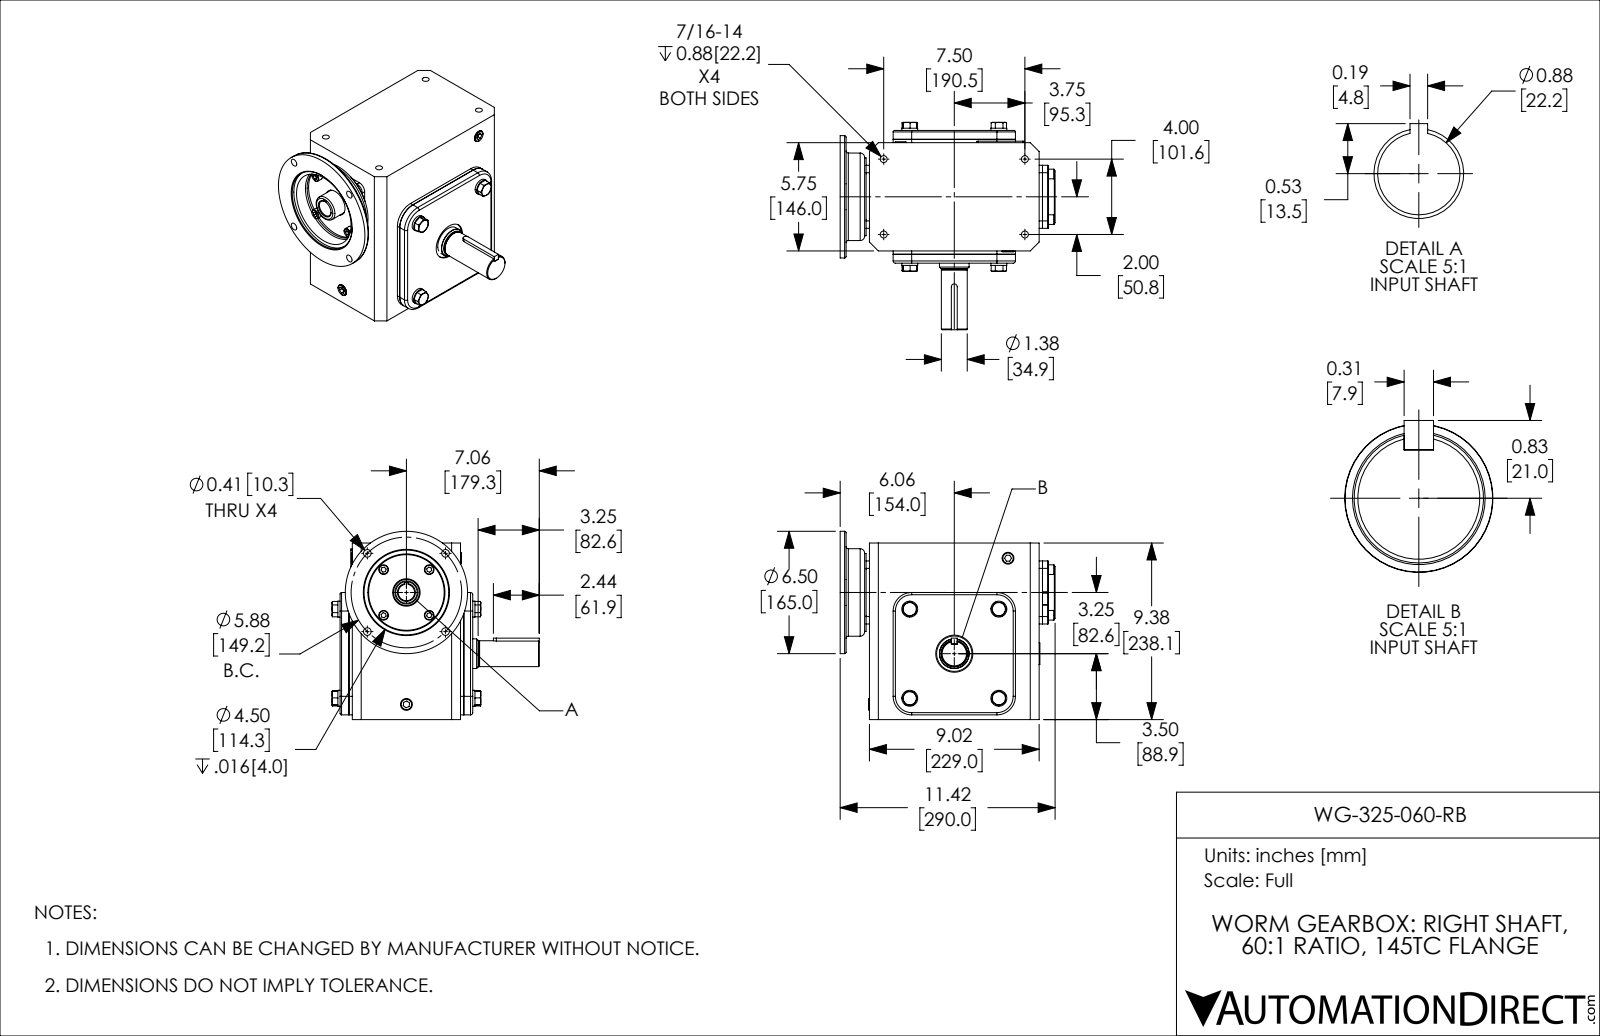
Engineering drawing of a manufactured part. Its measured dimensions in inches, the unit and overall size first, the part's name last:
Units: inches
Overall size (bounding box): 11.417 × 11.014 × 9.998
Round holes (diameter × count): ⌀0.368 ×4, ⌀0.406 ×4, ⌀0.628 ×3, ⌀0.591 ×1, ⌀0.875 ×1, ⌀0.978 ×1, ⌀1.181 ×1, ⌀1.457 ×1, ⌀1.969 ×1, ⌀2.441 ×1, ⌀2.756 ×1, ⌀4.016 ×1
Round bosses / shafts (diameter × count): ⌀0.846 ×4, ⌀0.512 ×4, ⌀6.496 ×1, ⌀4.646 ×1, ⌀4.134 ×1, ⌀2.835 ×1, ⌀1.575 ×1, ⌀1.378 ×1
Partial cylindrical surfaces — rounded edges, fillets, slot ends (radius × count): R0.079 ×11, R0.118 ×4, R0.394 ×4, R0.906 ×4, R0.984 ×4, R0.02 ×2, R0.039 ×2, R0.156 ×1
Main face-to-face distances: 0.079, 0.177, 6.496, 0.394, 6.969, 0.472, 6.575, 6.398, 0.571, 0.65
Hole centre spacings: 2.937, 4.154, 2.385, 4, 4.389, 5.718, 5.817, 5.875
Volume: 504 in³ · Surface area: 902.4 in²
Bodies: 39 solids, 576 faces (318 planar, 168 cylindrical, 90 other)
Part name (STEP PRODUCT): WG-325-060-RB
STEP written by: SolidWorks 2017 (AUTOMOTIVE_DESIGN)
